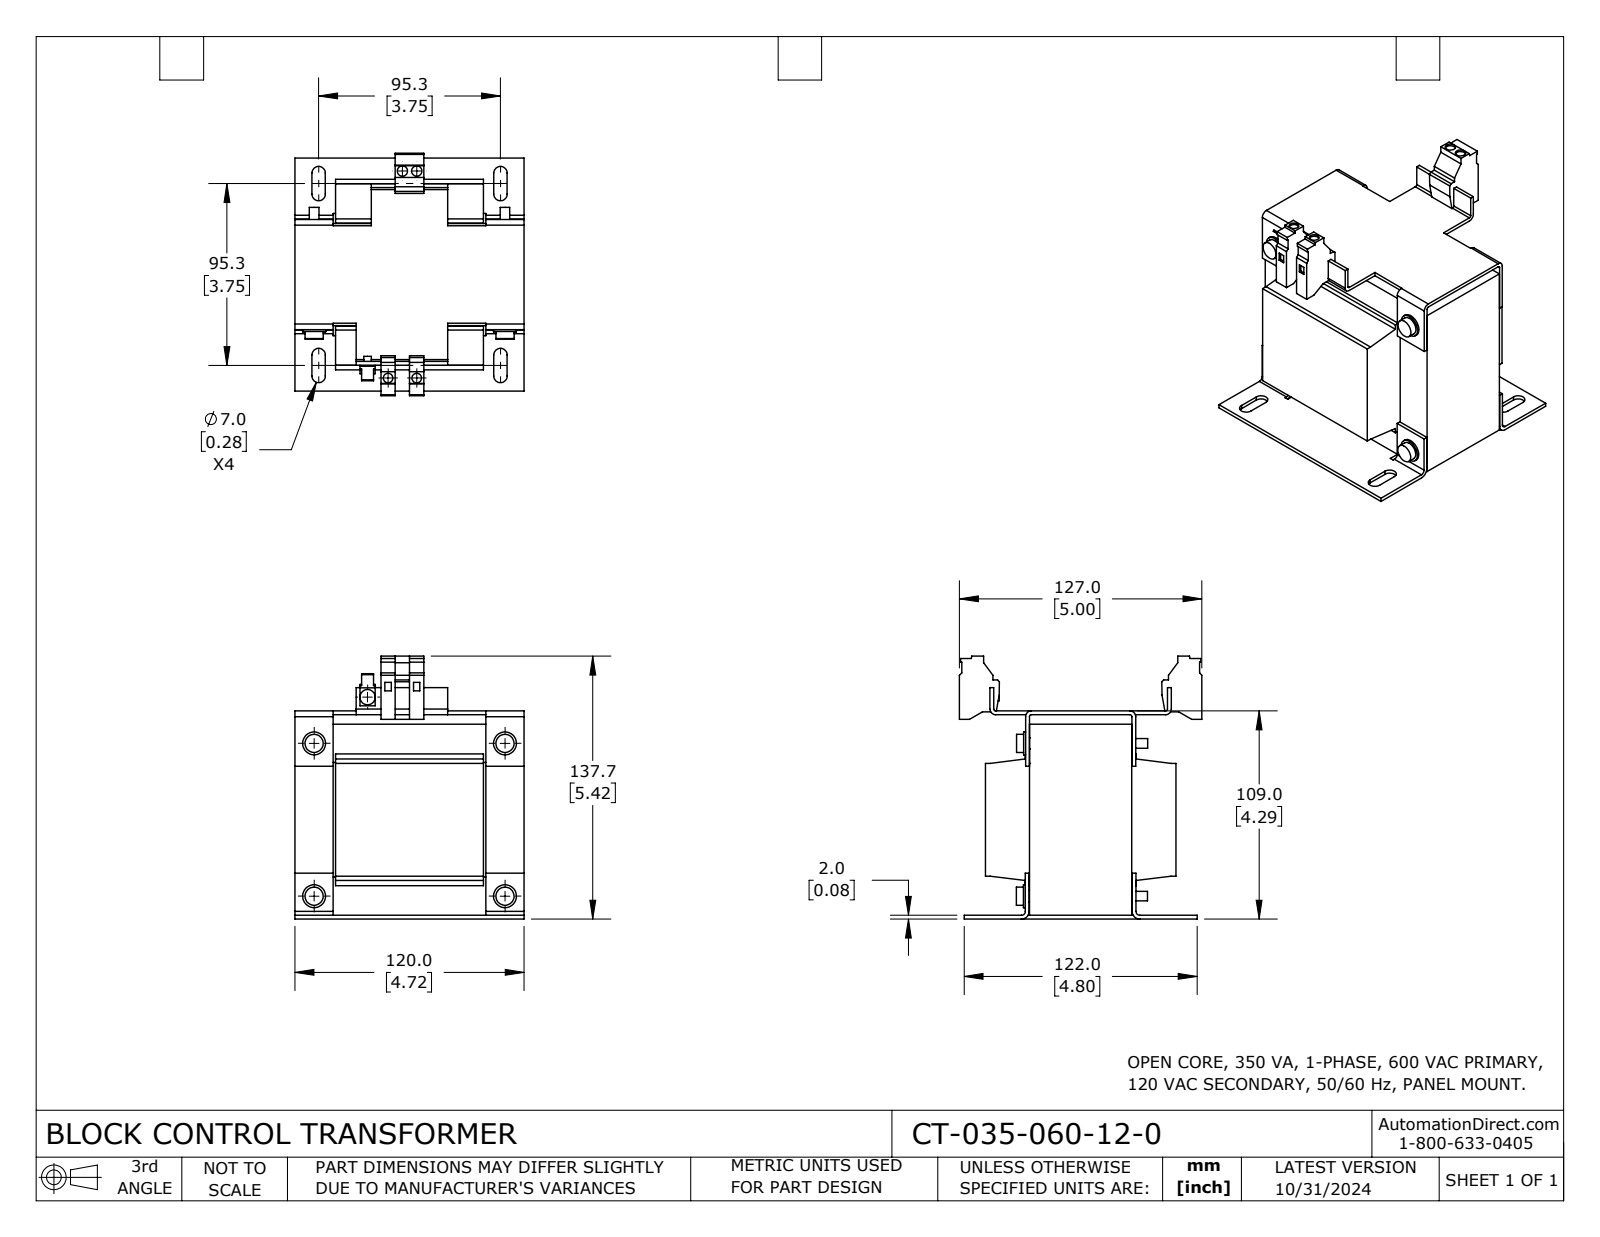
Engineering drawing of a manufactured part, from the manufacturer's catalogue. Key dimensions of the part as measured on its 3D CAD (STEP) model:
Part name (STEP PRODUCT): CT-035-060-12-0
STEP written by: SolidWorks 2023 (CONFIG_CONTROL_DESIGN)
Units: inches
Bodies: 1 solid, 322 faces (237 planar, 85 cylindrical, 0 other)
Overall size (bounding box): 5.421 × 5 × 4.724
Volume: 56.21 in³ · Surface area: 208.9 in²
Round holes (diameter × count): ⌀0.197 ×2, ⌀0.213 ×2
Round bosses / shafts (diameter × count): ⌀0.472 ×4, ⌀0.374 ×4, ⌀0.236 ×4, ⌀0.197 ×4, ⌀0.315 ×1, ⌀0.157 ×1
Partial cylindrical surfaces — rounded edges, fillets, slot ends (radius × count): R0.138 ×8, R0.039 ×4, R0.118 ×4, R0.079 ×2, R0.157 ×2
Main face-to-face distances: 0.079, 4.213, 3.937, 0.787, 0.837, 3.888, 0.911, 3.018, 3.1, 3.15
Hole centre spacings: 4.278, 0.295, 0.591, 4.268, 4.308
